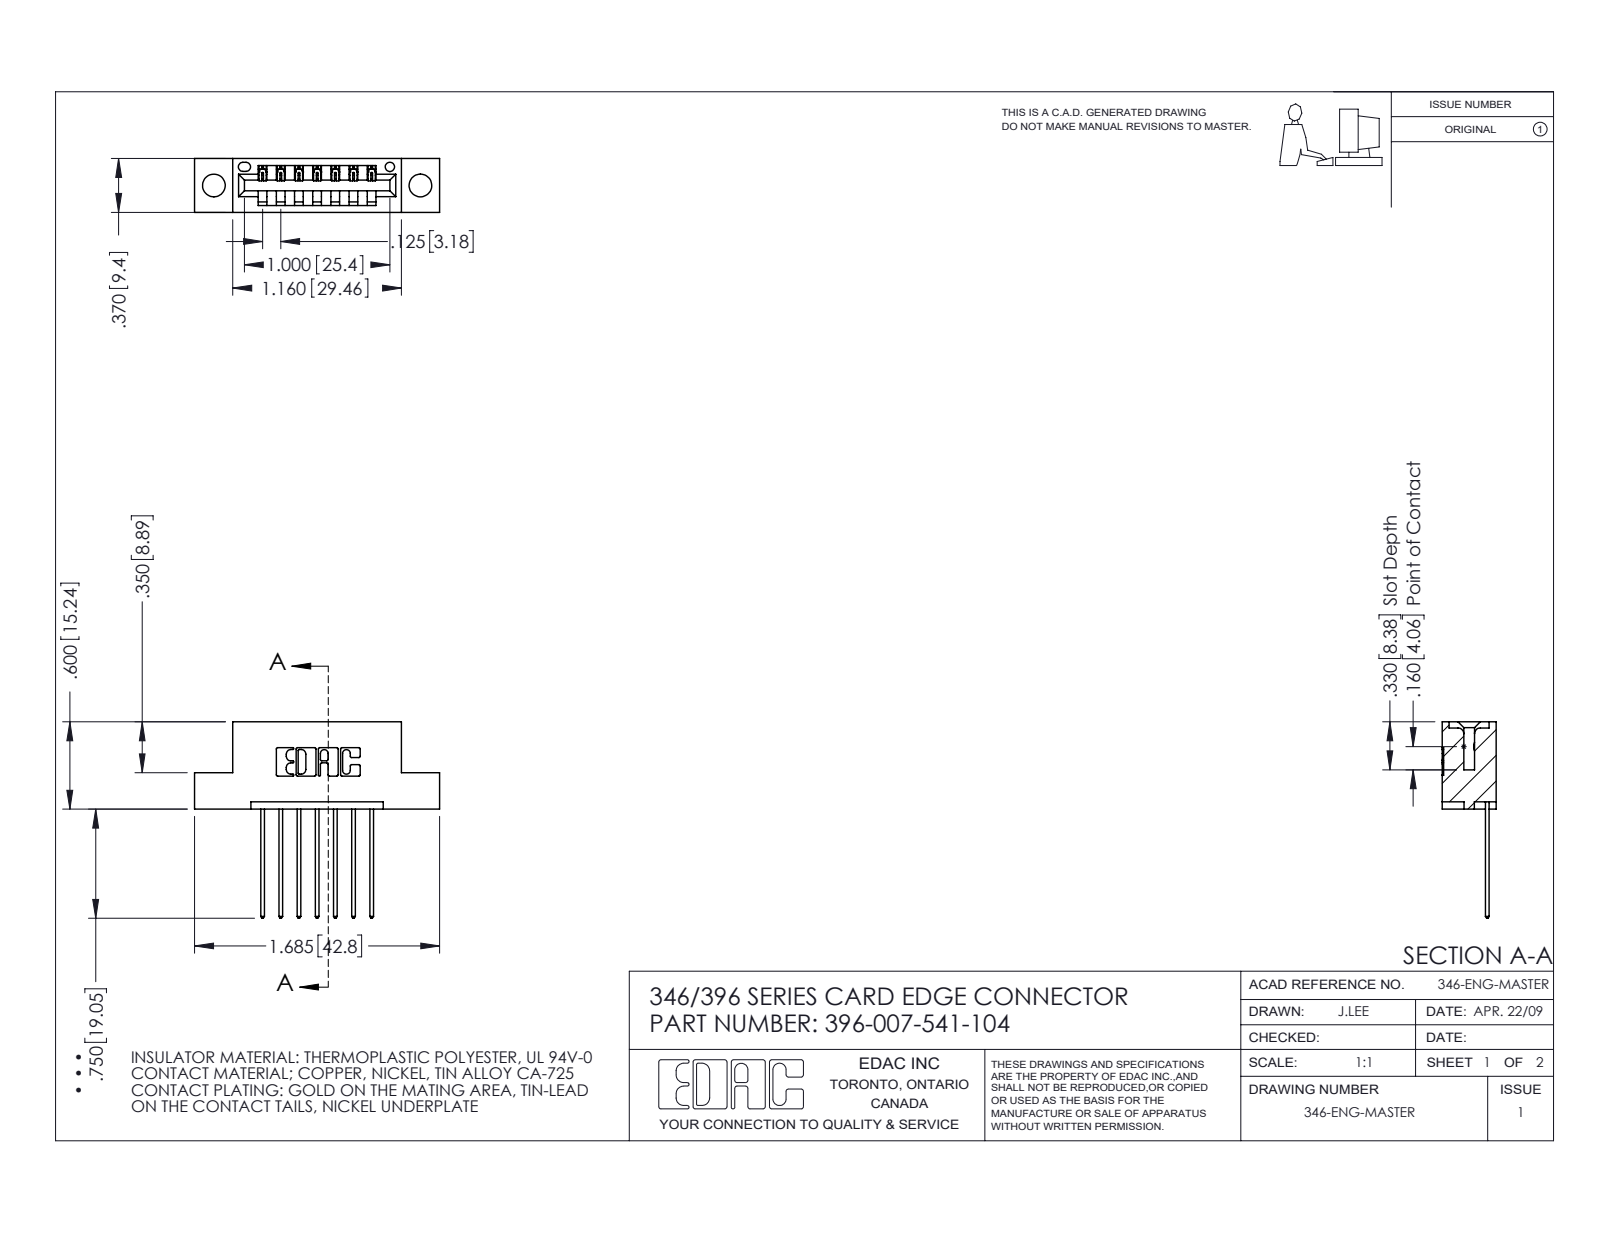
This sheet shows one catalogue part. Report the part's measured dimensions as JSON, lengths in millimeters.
{"part_name": "345-292-001_345-293-141; 396-007-541-104; 346 Part_Flush Mounting Lugs - 0.156 Dia-TH", "step_written_by": "SolidWorks 2016 (CONFIG_CONTROL_DESIGN)", "units": "millimeters", "bodies": {"solids": 8, "faces": 528, "planar": 356, "cylindrical": 172, "other": 0}, "overall_size": [42.8, 34.3, 9.4], "volume_mm3": 3790, "surface_area_mm2": 4303, "round_holes": [[4, 2], [1.6, 1]], "partial_cylinders_radius": [[0.3, 22], [0.2, 14], [0.3, 14], [0.2, 6], [0.8, 6], [0.7, 3], [0.8, 2], [1, 2]], "face_to_face_distances": [6.4, 1.2, 8.2, 9.4, 1.8, 7.6, 0.6, 3.8, 5.6, 2.5], "hole_center_spacings": [6.2, 30.9, 36.1]}
